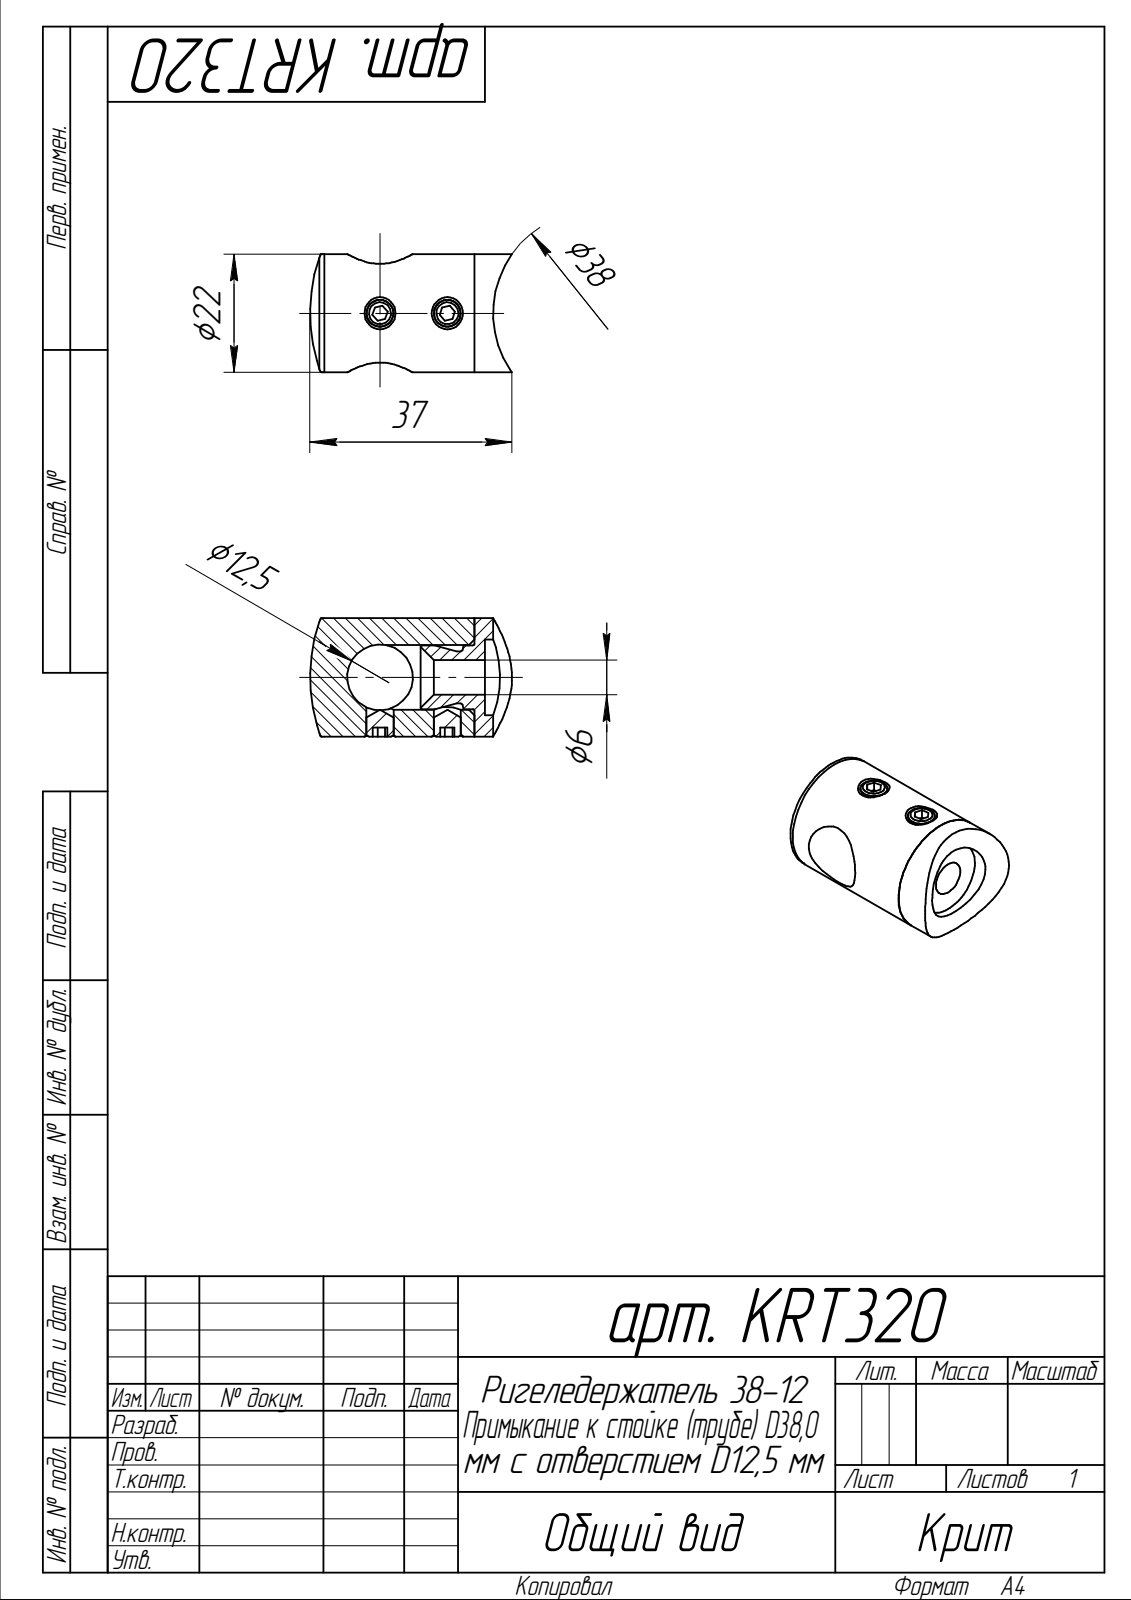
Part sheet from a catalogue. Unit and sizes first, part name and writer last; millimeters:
Units: millimetres
Overall size (bounding box): 37.5 × 22 × 22
Round holes (diameter × count): ⌀5 ×2, ⌀6.4 ×1, ⌀12 ×1, ⌀12.2 ×1, ⌀14 ×1
Round bosses / shafts (diameter × count): ⌀22 ×1, ⌀12.7 ×1, ⌀12.5 ×1, ⌀9.7 ×1
Partial cylindrical surfaces — rounded edges, fillets, slot ends (radius × count): R19 ×1
Main face-to-face distances: 2, 2.5, 10, 12, 1.7, 11.86, 2.52, 9.34, 14.36, 9.36
Hole centre spacings: 12.5
Volume: 9 267 mm³ · Surface area: 5 578 mm²
Bodies: 4 solids, 79 faces (22 planar, 27 cylindrical, 30 other)
Part name (STEP PRODUCT): арт. KRT320; socket set screw cone point_am_B18.3.6M - M5 x 0.8 x 5 Hex Socket Cone Pt. SS --N; арт. KRT320.001; арт. KRT320.002
STEP written by: SolidWorks 2014 (AUTOMOTIVE_DESIGN)
